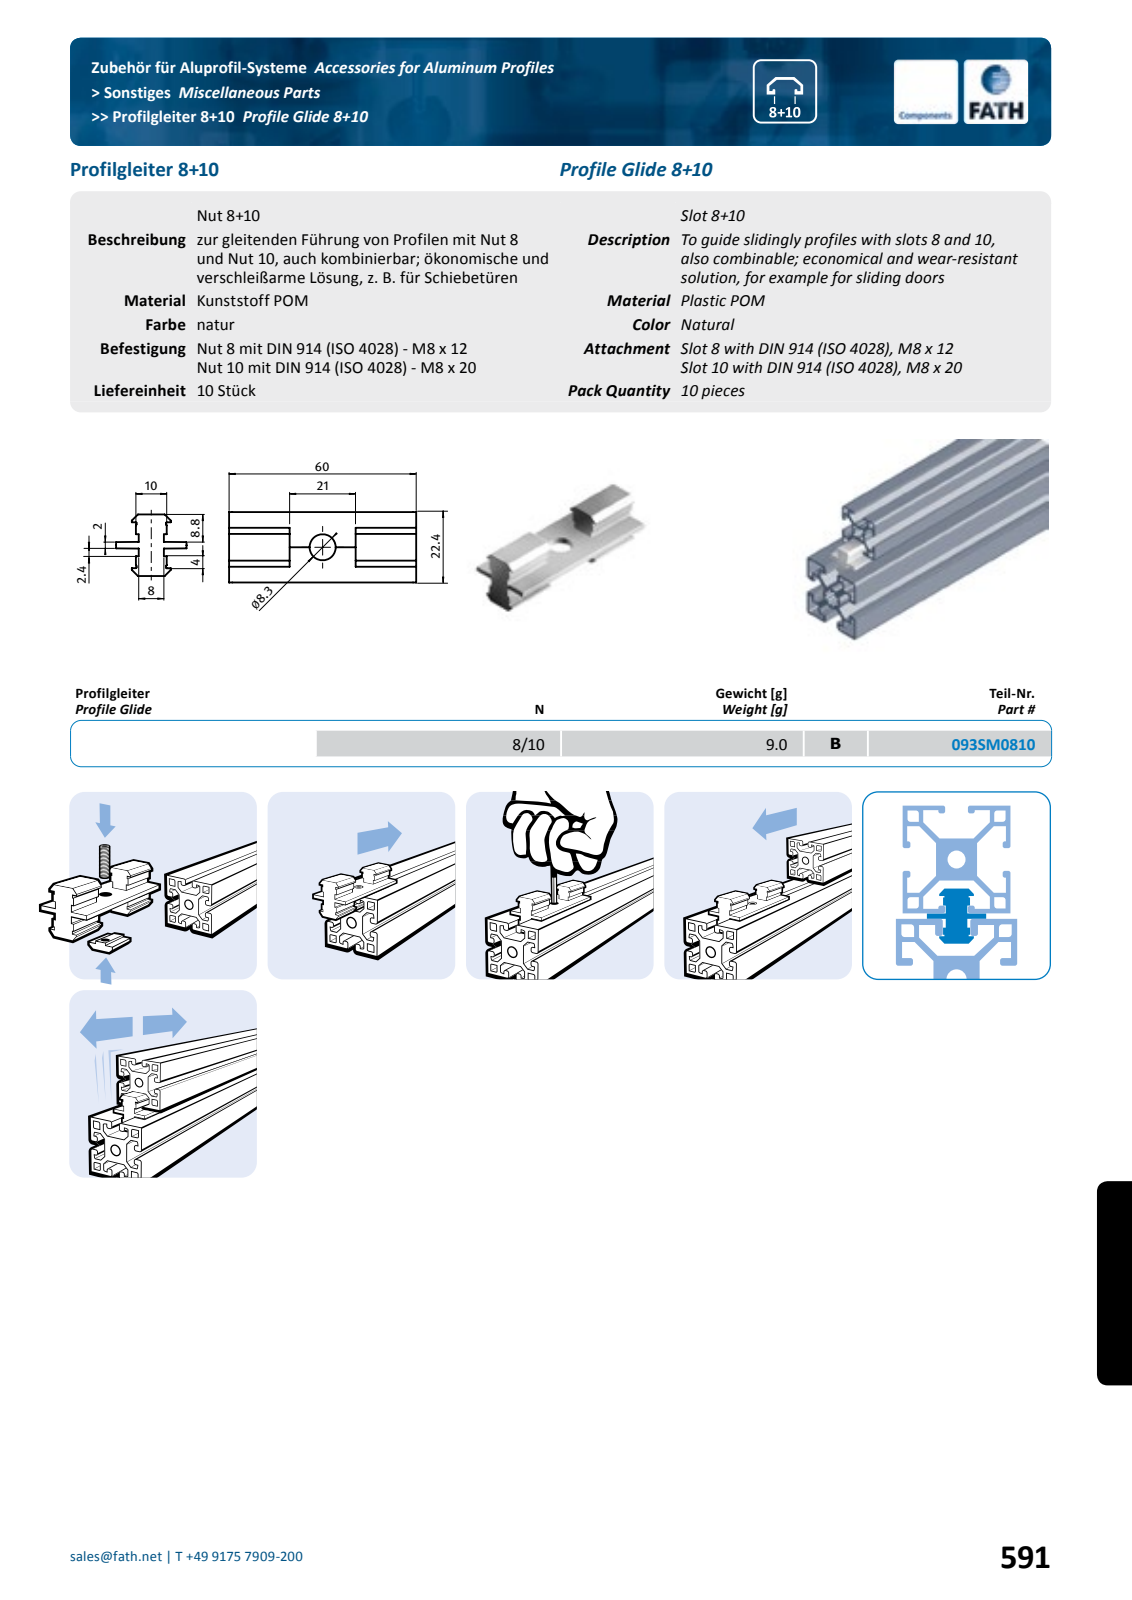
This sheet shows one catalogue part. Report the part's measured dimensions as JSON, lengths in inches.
{"part_name": "fath_093sm0810", "step_written_by": "Spatial InterOp 3D (automotive_design)", "units": "inches", "bodies": {"solids": 1, "faces": 476, "planar": 82, "cylindrical": 226, "other": 168}, "overall_size": [2.343, 0.882, 0.772], "volume_in3": 0.412, "surface_area_in2": 10.34, "round_holes": [[0.327, 1]], "partial_cylinders_radius": [[0.008, 116], [0.02, 14], [0.039, 8]], "face_to_face_distances": [0.087, 1.585, 0.035, 0.35, 0.758, 0.248, 0.386, 0.782, 0.283, 0.598]}
